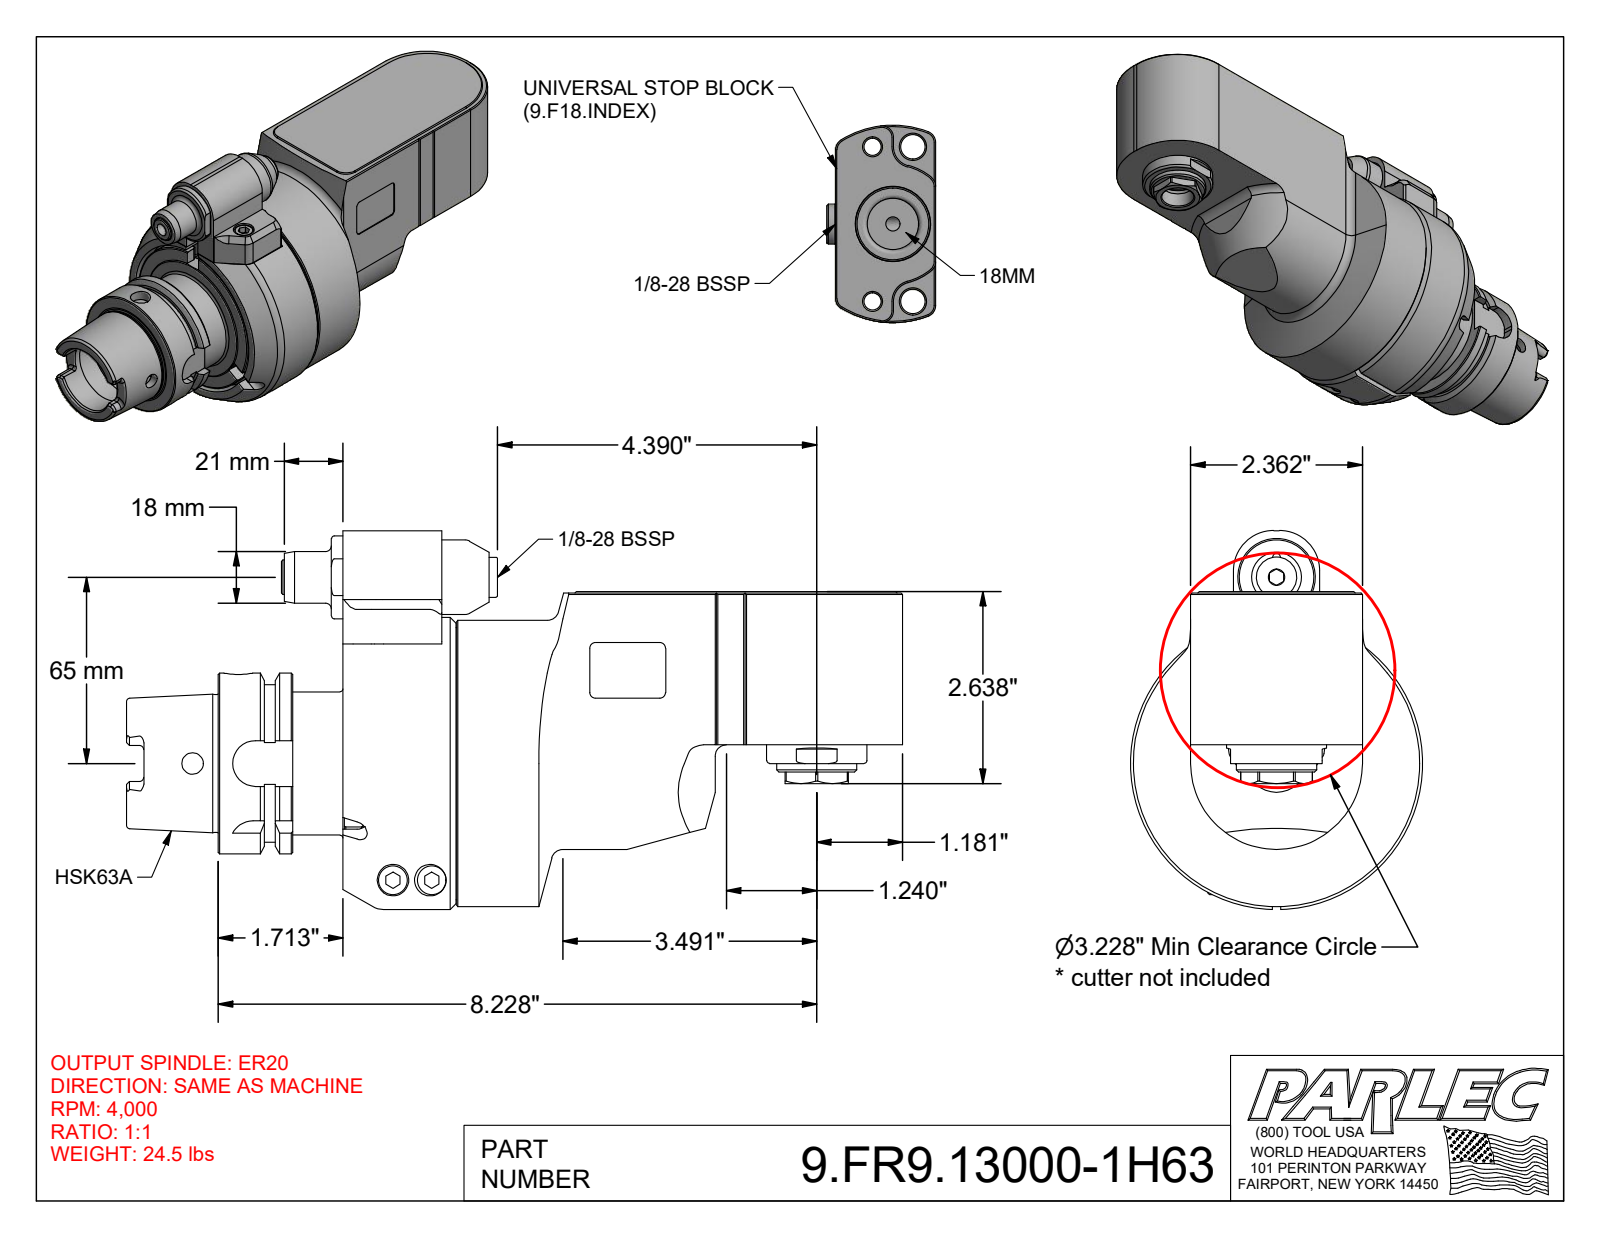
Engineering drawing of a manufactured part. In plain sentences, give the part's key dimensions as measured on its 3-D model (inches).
The part is named "9.FR9.13000-1H63; 9_FR9_13000; 9_GA1_566_2 (Type 1, H63A, 65mm)". Its 3-D file was written by "Autodesk Inventor 2020 (AUTOMOTIVE_DESIGN)". It is 5 solids with 488 faces: 244 planar, 118 cylindrical and 126 other. Overall it measures 10.669 by 5.206 by 4.016 inches. Its volume is 72.12 cubic inches and its surface area 236.3 square inches. Round holes: 2 of diameter 0.102, 2 of diameter 0.165, 2 of diameter 0.197, 2 of diameter 0.409, 2 of diameter 0.433, 2 of diameter 0.492, 1 of diameter 0.098, 1 of diameter 0.118, 1 of diameter 0.157, 1 of diameter 0.256, 1 of diameter 0.276, 1 of diameter 0.295. Round bosses or shafts: 4 of diameter 0.394, 4 of diameter 0.236, 2 of diameter 0.709, 1 of diameter 4.016, 1 of diameter 3.937, 1 of diameter 3.74, 1 of diameter 3.031, 1 of diameter 2.48. Partial cylindrical surfaces (rounded edges, fillets, slot ends): 6 of radius 0.059, 5 of radius 0.157, 4 of radius 0.079, 4 of radius 0.113, 4 of radius 0.315, 2 of radius 0.02, 2 of radius 0.039, 2 of radius 0.138. The main face-to-face distances are 1.22, 2.362, 1.024, 0.039, 0.02, 1.26, 0.719, 0.276, 0.335, 1.555. The hole center spacings are 0.276, 7.953, 0.049, 0.512, 0.551, 1.72, 2.208, 2.283.
